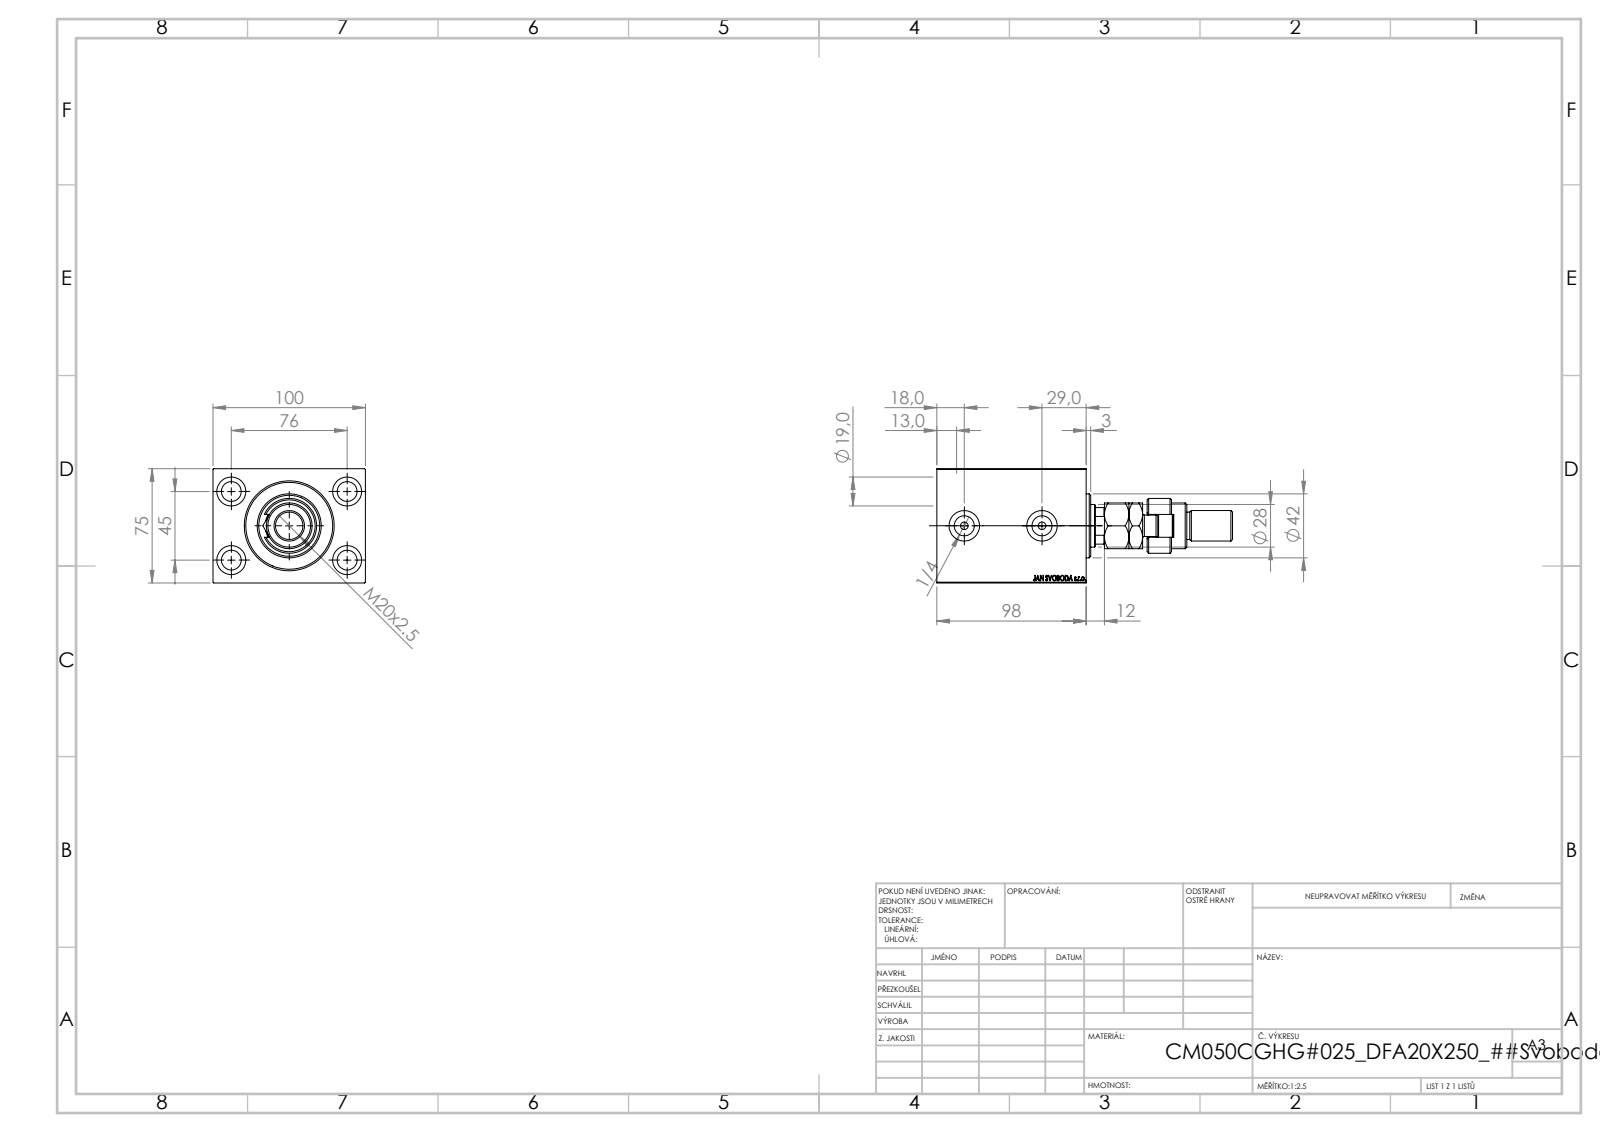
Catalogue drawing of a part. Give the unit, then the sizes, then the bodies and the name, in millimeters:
Units: millimetres
Overall size (bounding box): 194 × 100 × 75
Round holes (diameter × count): ⌀13 ×4, ⌀19 ×4, ⌀5 ×2, ⌀13.16 ×2, ⌀20 ×2, ⌀18.5 ×1, ⌀28 ×1, ⌀31.5 ×1, ⌀50 ×1, ⌀52 ×1, ⌀57 ×1
Round bosses / shafts (diameter × count): ⌀42 ×1, ⌀36 ×1, ⌀30 ×1, ⌀22 ×1, ⌀20 ×1, ⌀18 ×1, ⌀14 ×1
Partial cylindrical surfaces — rounded edges, fillets, slot ends (radius × count): R7.5 ×1, R12 ×1, R13.5 ×1
Main face-to-face distances: 75, 100, 98, 84, 14, 12, 25, 37, 72, 49
Hole centre spacings: 44.16, 45, 76, 88.32, 51
Volume: 679 900 mm³ · Surface area: 118 719 mm²
Bodies: 5 solids, 950 faces (437 planar, 75 cylindrical, 438 other)
Part name (STEP PRODUCT): MFA; V450CM_VC_B; V450CM_C_Body; V450CM_C_VCP (+1 more)
STEP written by: SolidWorks 2019 (CONFIG_CONTROL_DESIGN)
